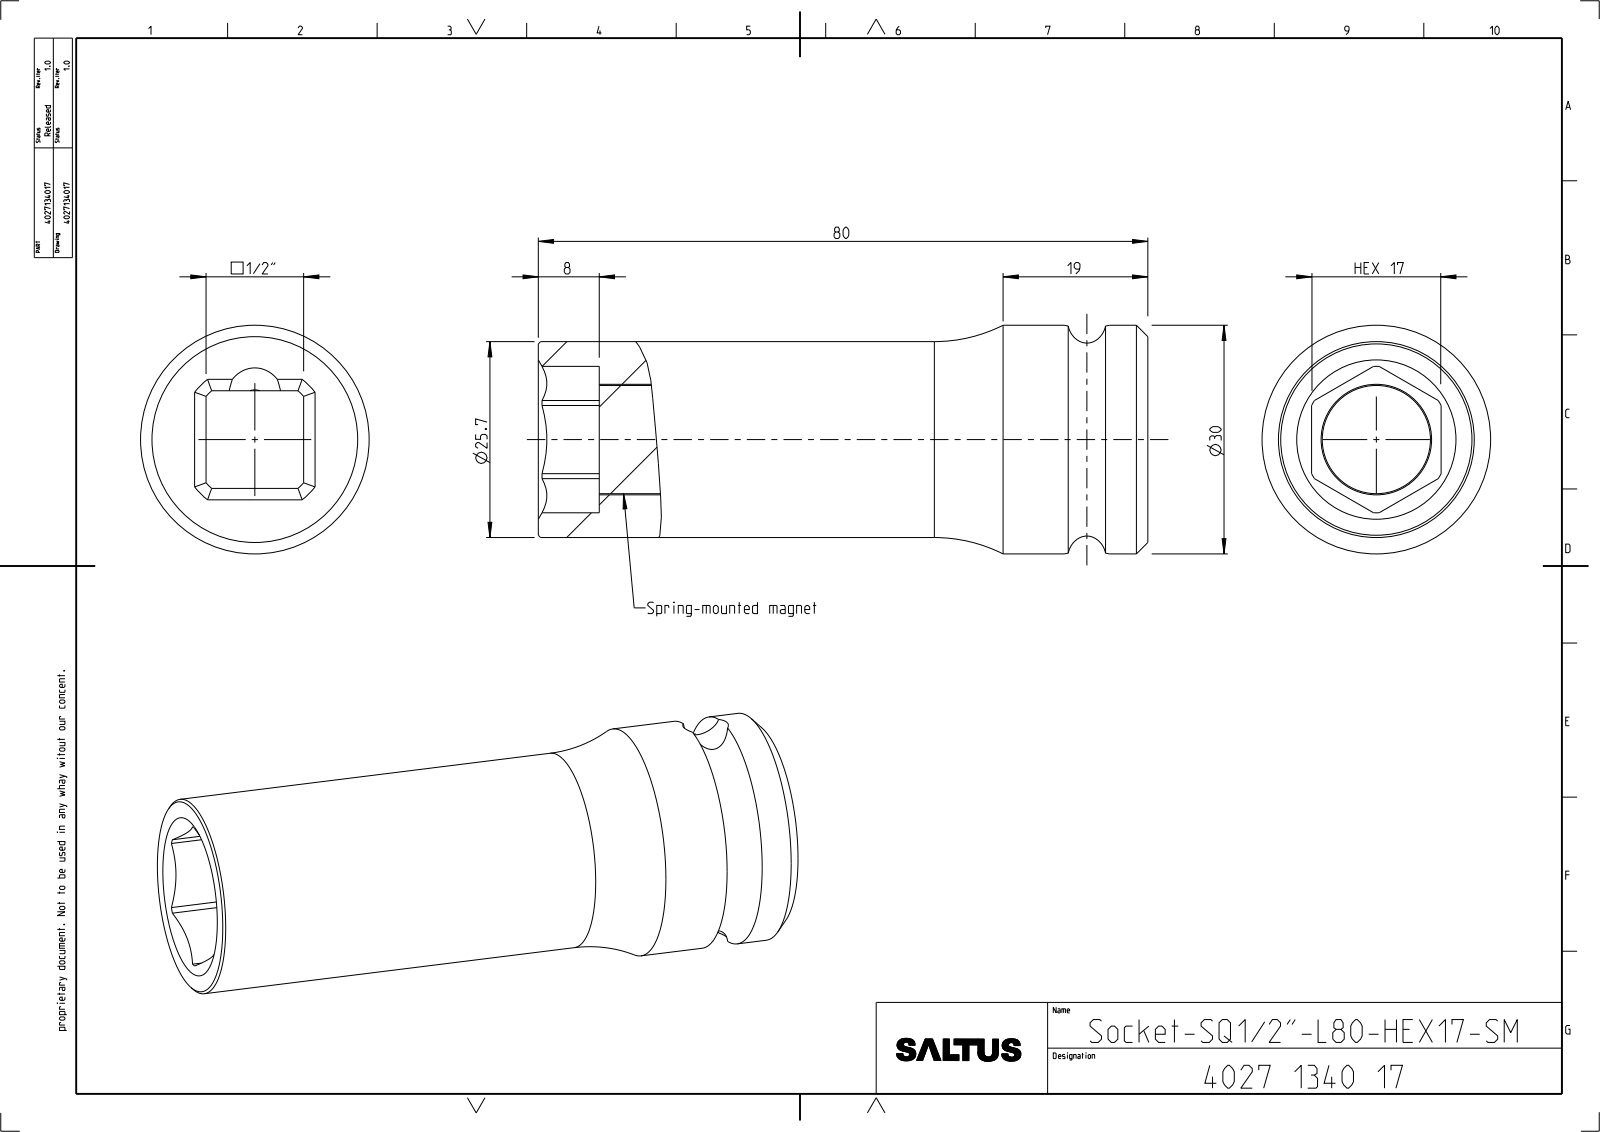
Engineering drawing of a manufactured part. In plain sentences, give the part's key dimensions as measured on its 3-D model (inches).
The part is named "4027134017". Its 3-D file was written by "CREO PARAMETRIC BY PTC INC, 2022414 (CONFIG_CONTROL_DESIGN)". It is 2 solids with 62 faces: 21 planar, 25 cylindrical and 16 other. Overall it measures 3.15 by 1.181 by 1.181 inches. Its volume is 2.107 cubic inches and its surface area 18.83 square inches. Round holes: 1 of diameter 0.236, 1 of diameter 0.571. Round bosses or shafts: 1 of diameter 1.181, 1 of diameter 1.012, 1 of diameter 0.559. Partial cylindrical surfaces (rounded edges, fillets, slot ends): 1 of radius 0.157, 1 of radius 0.337, 1 of radius 0.378. The main face-to-face distances are 0.505, 2.835, 0.669, 0.63, 2.205, 2.362, 1.732, 0.472, 3.15, 2.52.
